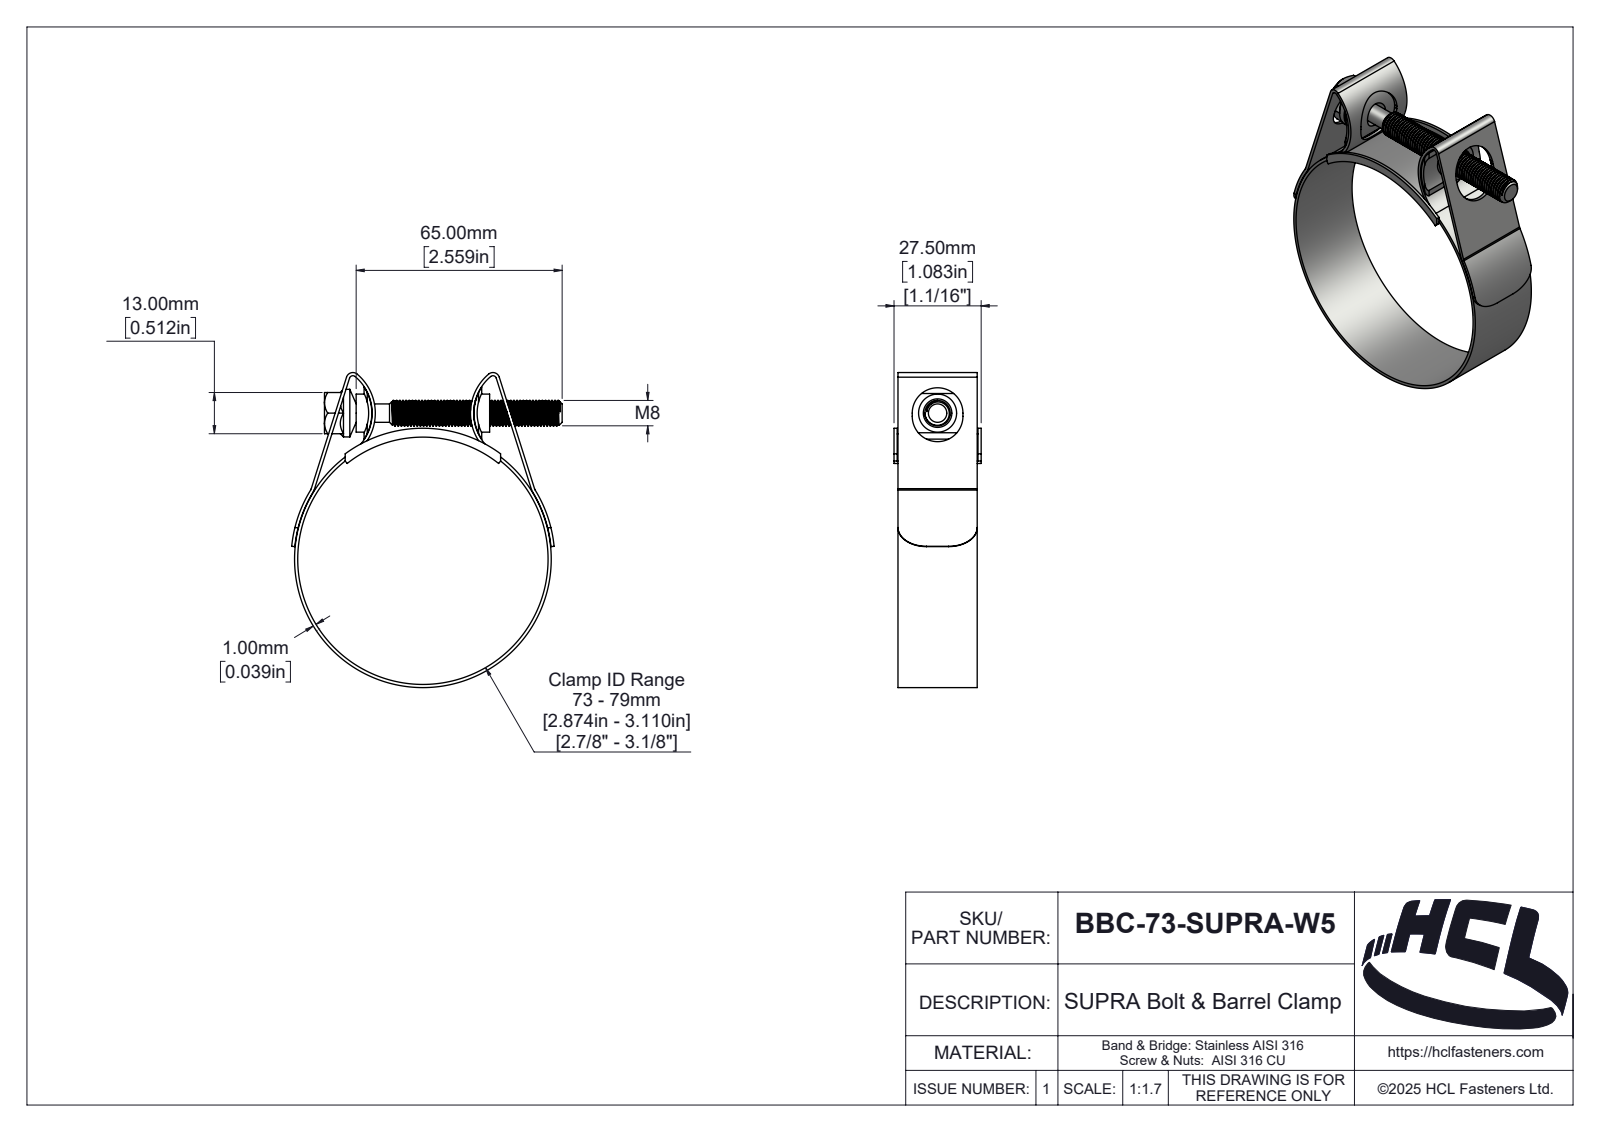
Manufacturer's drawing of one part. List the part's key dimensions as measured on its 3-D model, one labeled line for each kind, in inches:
Part name (STEP PRODUCT): BBC-73-SUPRA-W5
STEP written by: SolidWorks 2025 (AUTOMOTIVE_DESIGN)
Units: inches
Bodies: 5 solids, 350 faces (46 planar, 218 cylindrical, 86 other)
Overall size (bounding box): 3.912 × 3.36 × 1.083
Volume: 0.935 in³ · Surface area: 41.06 in²
Round holes (diameter × count): ⌀3.11 ×1
Round bosses / shafts (diameter × count): ⌀3.189 ×1, ⌀0.591 ×1, ⌀0.472 ×1, ⌀0.315 ×1, ⌀0.228 ×1
Partial cylindrical surfaces — rounded edges, fillets, slot ends (radius × count): R0.039 ×4, R0.043 ×2, R0.079 ×2, R0.083 ×2, R0.118 ×2, R0.315 ×2, R0.55 ×2, R0.59 ×2
Main face-to-face distances: 0.039, 0.984, 0.049, 1.033, 1.043, 0.994, 1.083, 0.512, 0.098, 1.56
